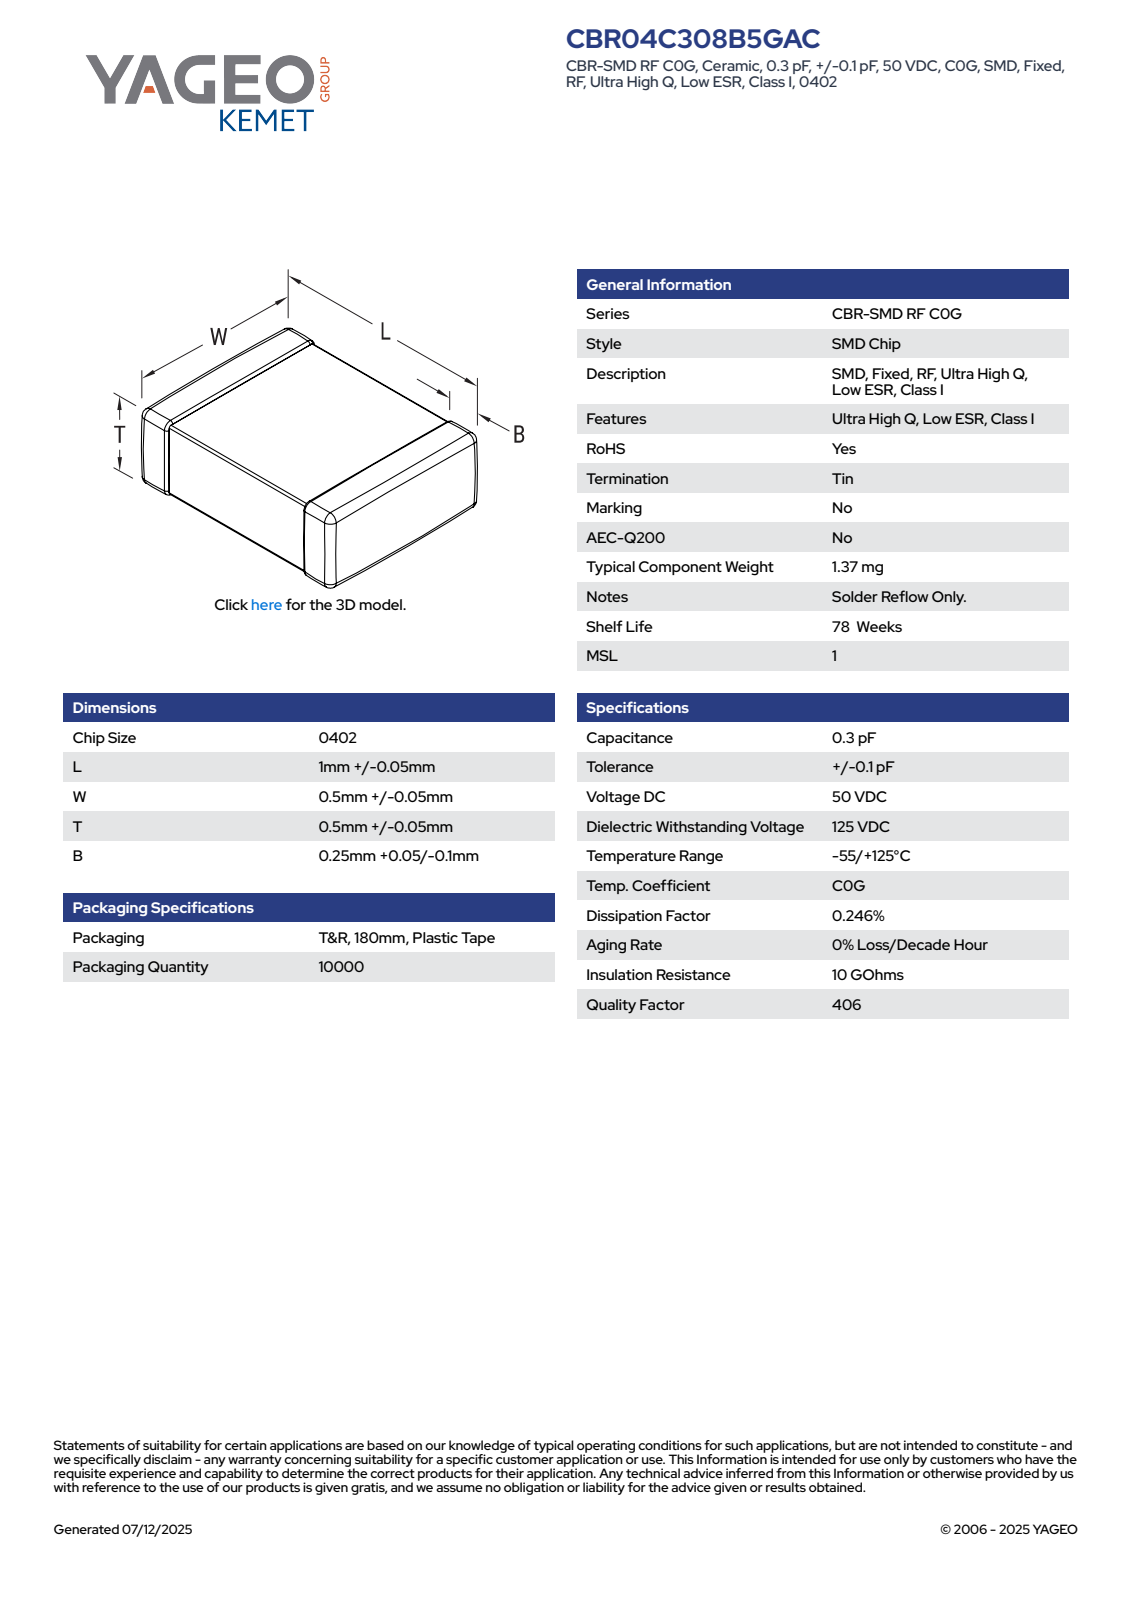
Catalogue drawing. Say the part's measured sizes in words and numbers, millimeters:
The part is named "CCS_CCSTDNOS_0402_L1.05W0.55T0.55B0.3". Its 3-D file was written by "SolidWorks 2014 (AUTOMOTIVE_DESIGN)". It is 4 solids with 121 faces: 71 planar, 34 cylindrical and 16 other. Overall it measures 1.05 by 0.55 by 0.55 millimeters. Its volume is 0.306 cubic millimeters and its surface area 3 square millimeters. The main face-to-face distances are 0.54, 0.55, 0.53, 1.05, 0.31, 0.32, 0.34.
